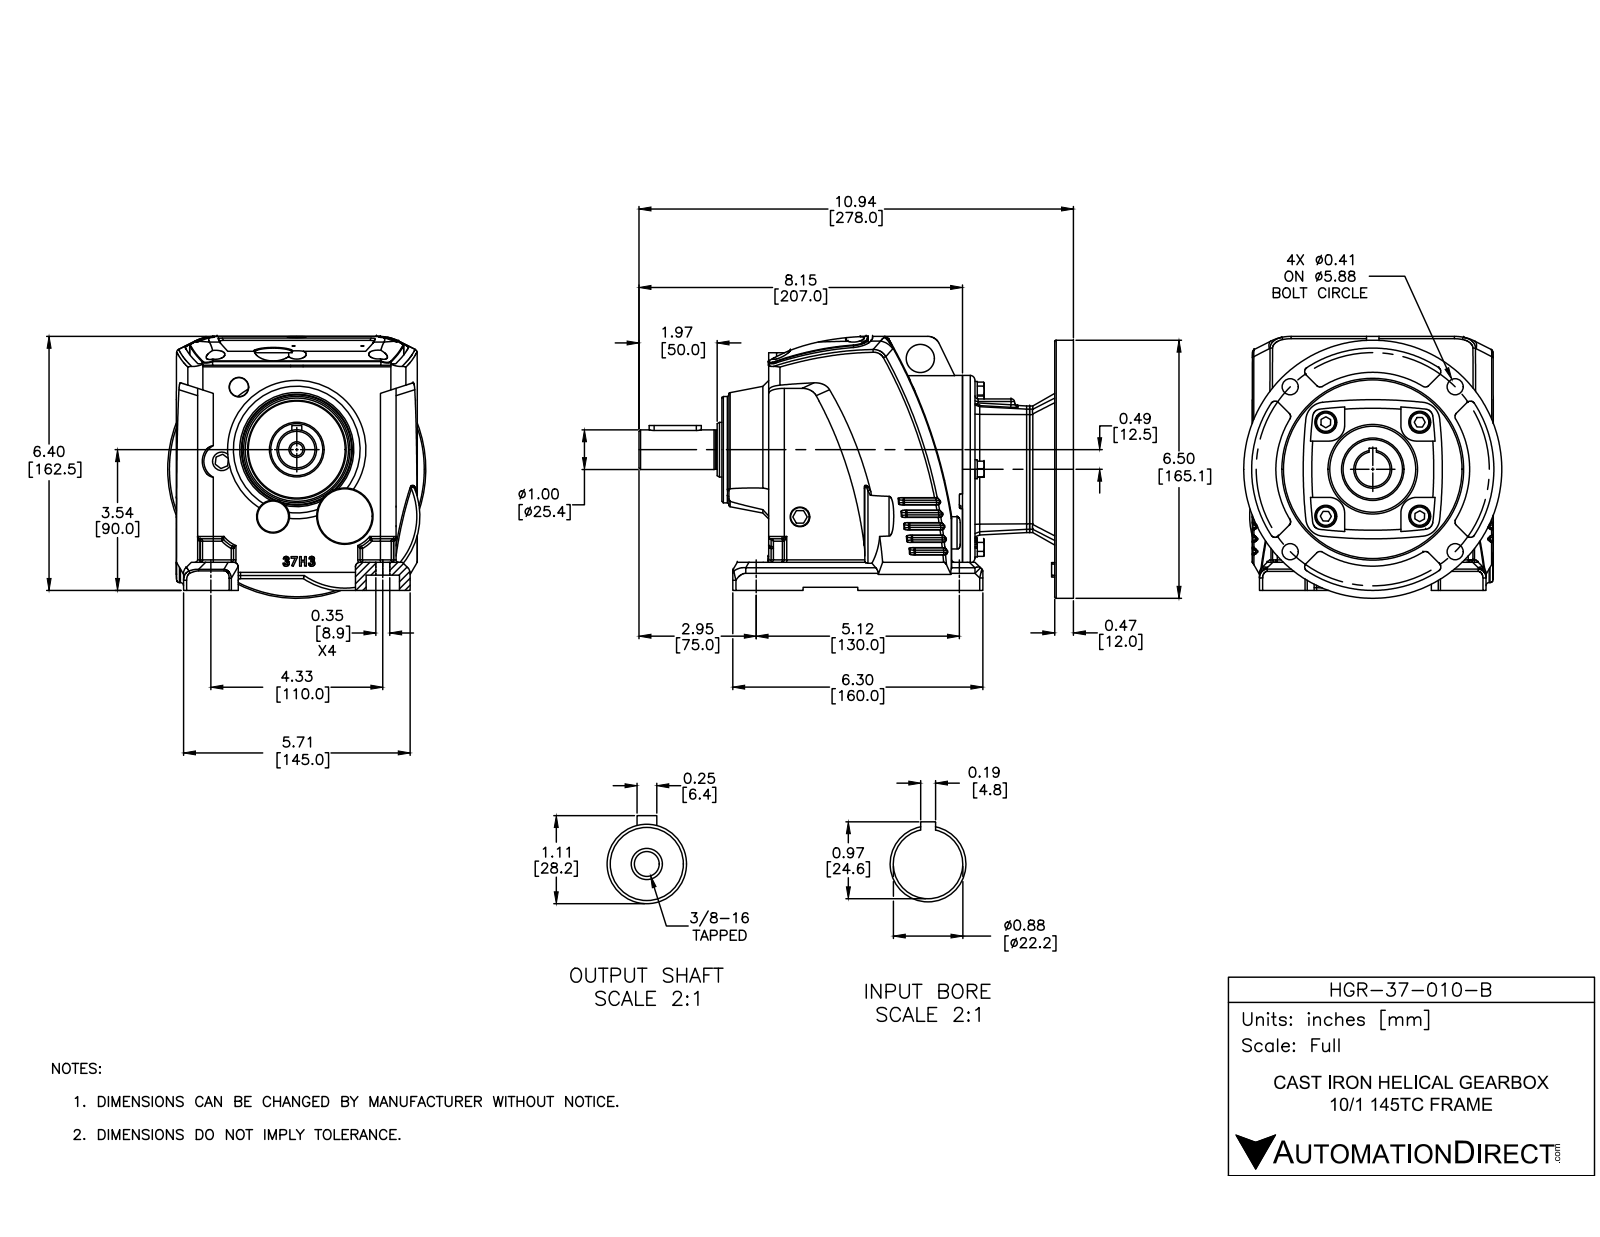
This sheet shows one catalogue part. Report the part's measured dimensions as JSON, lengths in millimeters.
{"part_name": "HGR-37-010-B", "step_written_by": "SolidWorks 2015 (CONFIG_CONTROL_DESIGN)", "units": "millimeters", "bodies": {"solids": 28, "faces": 1025, "planar": 348, "cylindrical": 289, "other": 388}, "overall_size": [278, 167.5, 165.1], "volume_mm3": 3066000, "surface_area_mm2": 308500, "round_holes": [[12, 6], [10.3, 4], [14, 4], [7, 3], [2, 2], [9, 2], [10, 2], [8, 1], [13.5, 1], [18, 1], [22.2, 1], [35, 1]], "round_bosses_or_shafts": [[13, 7], [12.2, 4], [165.1, 1], [120, 1], [68, 1], [62, 1], [55, 1], [35, 1]], "partial_cylinders_radius": [[1.5, 43], [3, 19], [2, 18], [10, 10], [5, 8], [8, 5], [4, 4], [7, 4]], "face_to_face_distances": [7, 16, 59, 28, 190, 43, 183, 8, 23, 66], "hole_center_spacings": [32.1, 42.5, 74.6, 85.9, 85.9, 117.1, 34.8, 47.4]}
